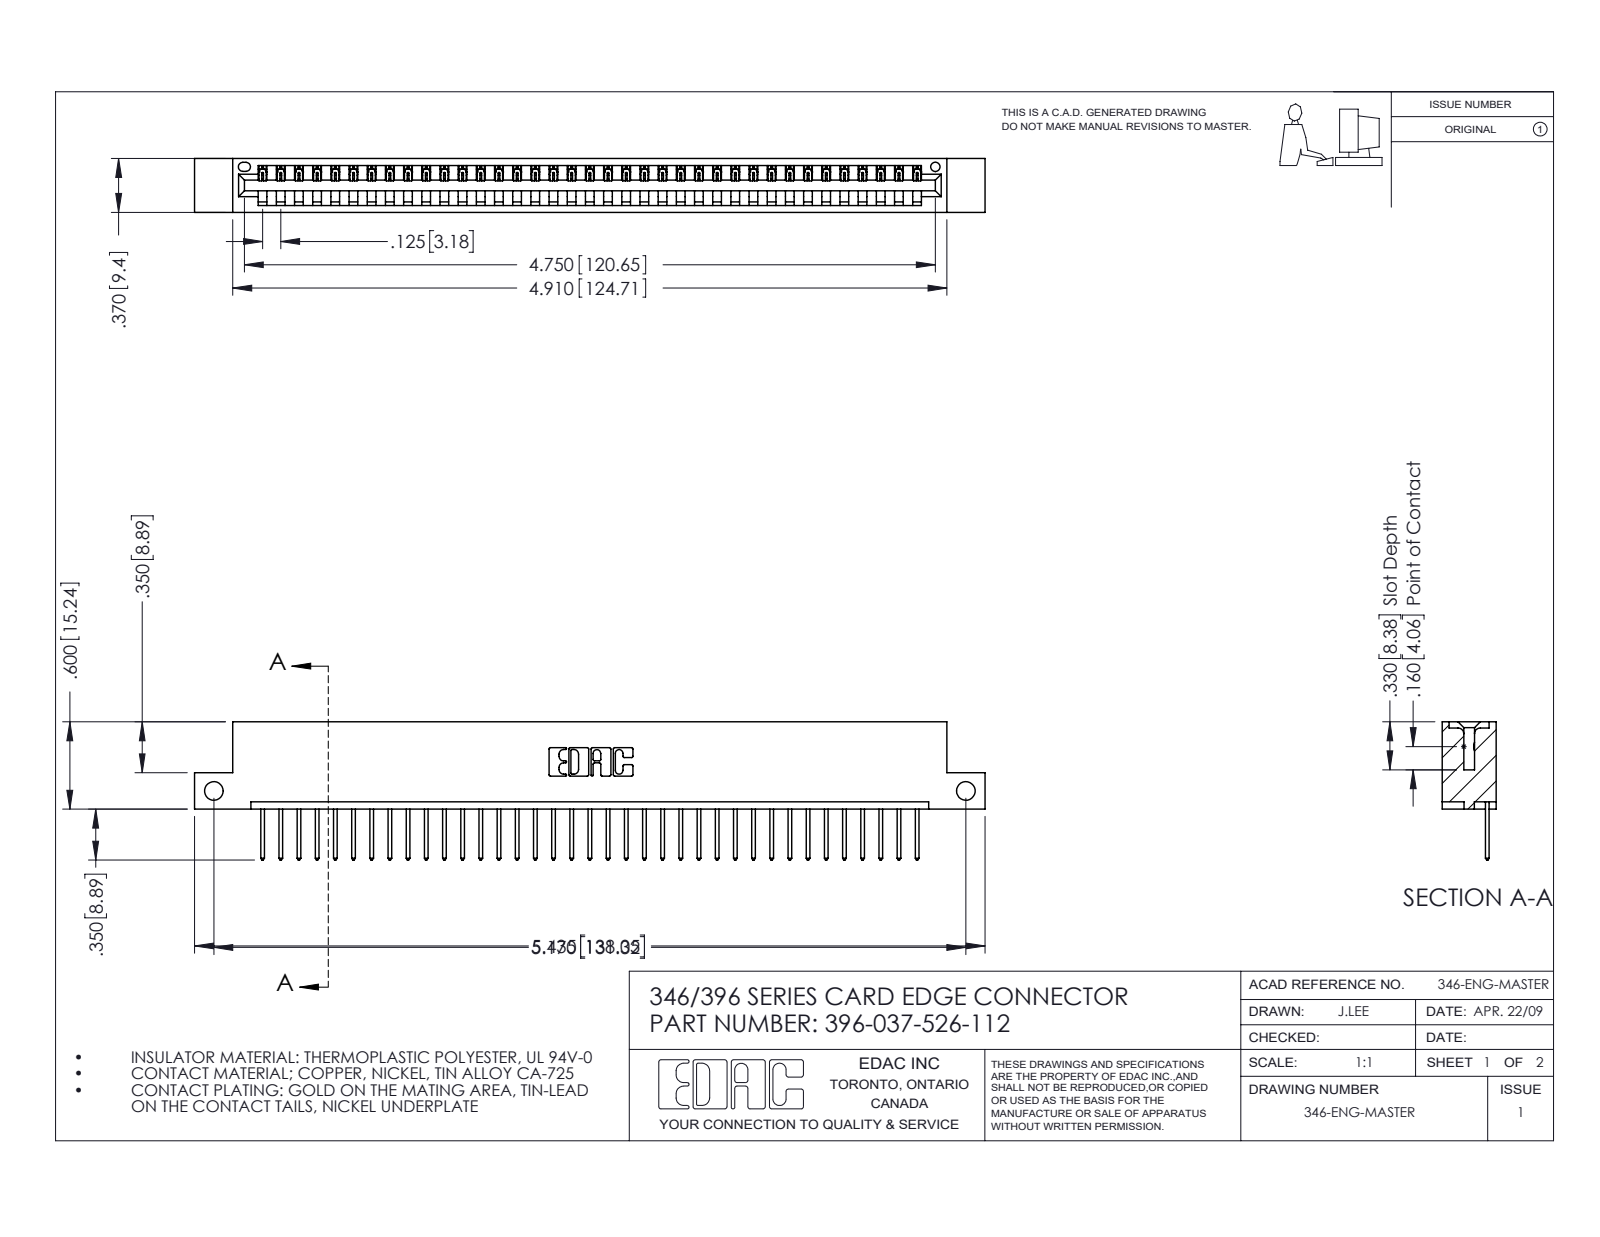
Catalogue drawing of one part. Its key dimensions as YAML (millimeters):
part_name: "345-292-001_345-293-126; 346 Part_Flush Mounting Lugs - Side Mount; 396-037-526-112"
step_written_by: "SolidWorks 2016 (CONFIG_CONTROL_DESIGN)"
units: millimeters
bodies: {solids: 38, faces: 2268, planar: 1556, cylindrical: 712, other: 0}
overall_size: [138, 24.1, 9.4]
volume: 13100
surface_area: 16090
round_holes:
  - {diameter: 3.3, count: 2}
  - {diameter: 1.6, count: 1}
partial_cylinders:
  - {radius: 0.2, count: 74}
  - {radius: 0.3, count: 74}
  - {radius: 0.3, count: 22}
  - {radius: 0.2, count: 6}
  - {radius: 0.8, count: 6}
  - {radius: 0.7, count: 3}
  - {radius: 0.8, count: 2}
  - {radius: 1, count: 2}
face_to_face_distances: [1.2, 8.2, 9.4, 6.4, 1.8, 7.6, 0.6, 3.8, 5.6, 2.5]
hole_center_spacings: [131.3]
